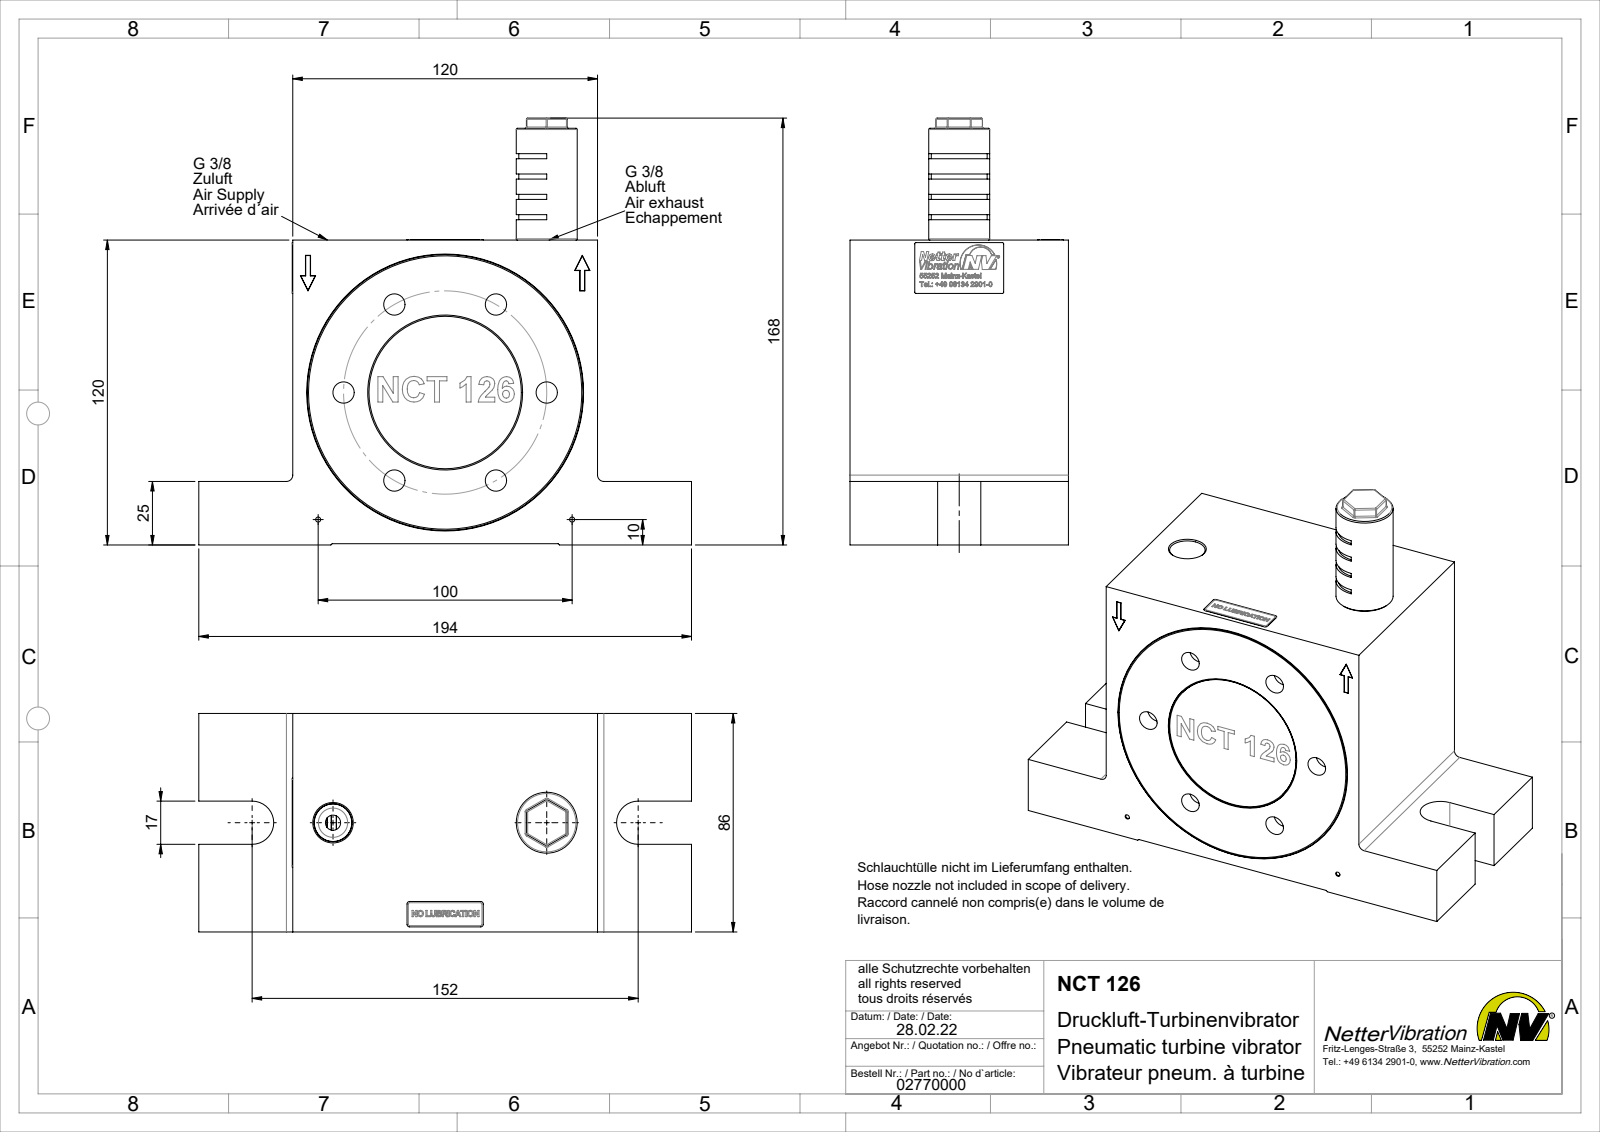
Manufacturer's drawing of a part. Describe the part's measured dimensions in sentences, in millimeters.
The part is named "NCT 126 Turbinenvibrator #02770000". Its 3-D file was written by "SolidWorks 2015 (AUTOMOTIVE_DESIGN)". It is 6 solids with 339 faces: 209 planar, 77 cylindrical and 53 other. Overall it measures 194 by 168 by 86.25 millimeters. Its volume is 1 487 000 cubic millimeters and its surface area 132 296 square millimeters. Round holes: 6 of diameter 8.4, 2 of diameter 2, 2 of diameter 15, 1 of diameter 61, 1 of diameter 106.5. Round bosses or shafts: 1 of diameter 109, 1 of diameter 106.47, 1 of diameter 103.87, 1 of diameter 60, 1 of diameter 24, 1 of diameter 16.66. Partial cylindrical surfaces (rounded edges, fillets, slot ends): 22 of radius 0.5, 4 of radius 1, 2 of radius 2.5, 2 of radius 8.5, 1 of radius 11. The main face-to-face distances are 120, 0.5, 76, 65.25, 10.75, 119.5, 10, 86, 20.75, 24.5. The hole center spacings are 40, 69.28, 80, 32.45, 48.05, 68.62, 71.08, 86.98.
